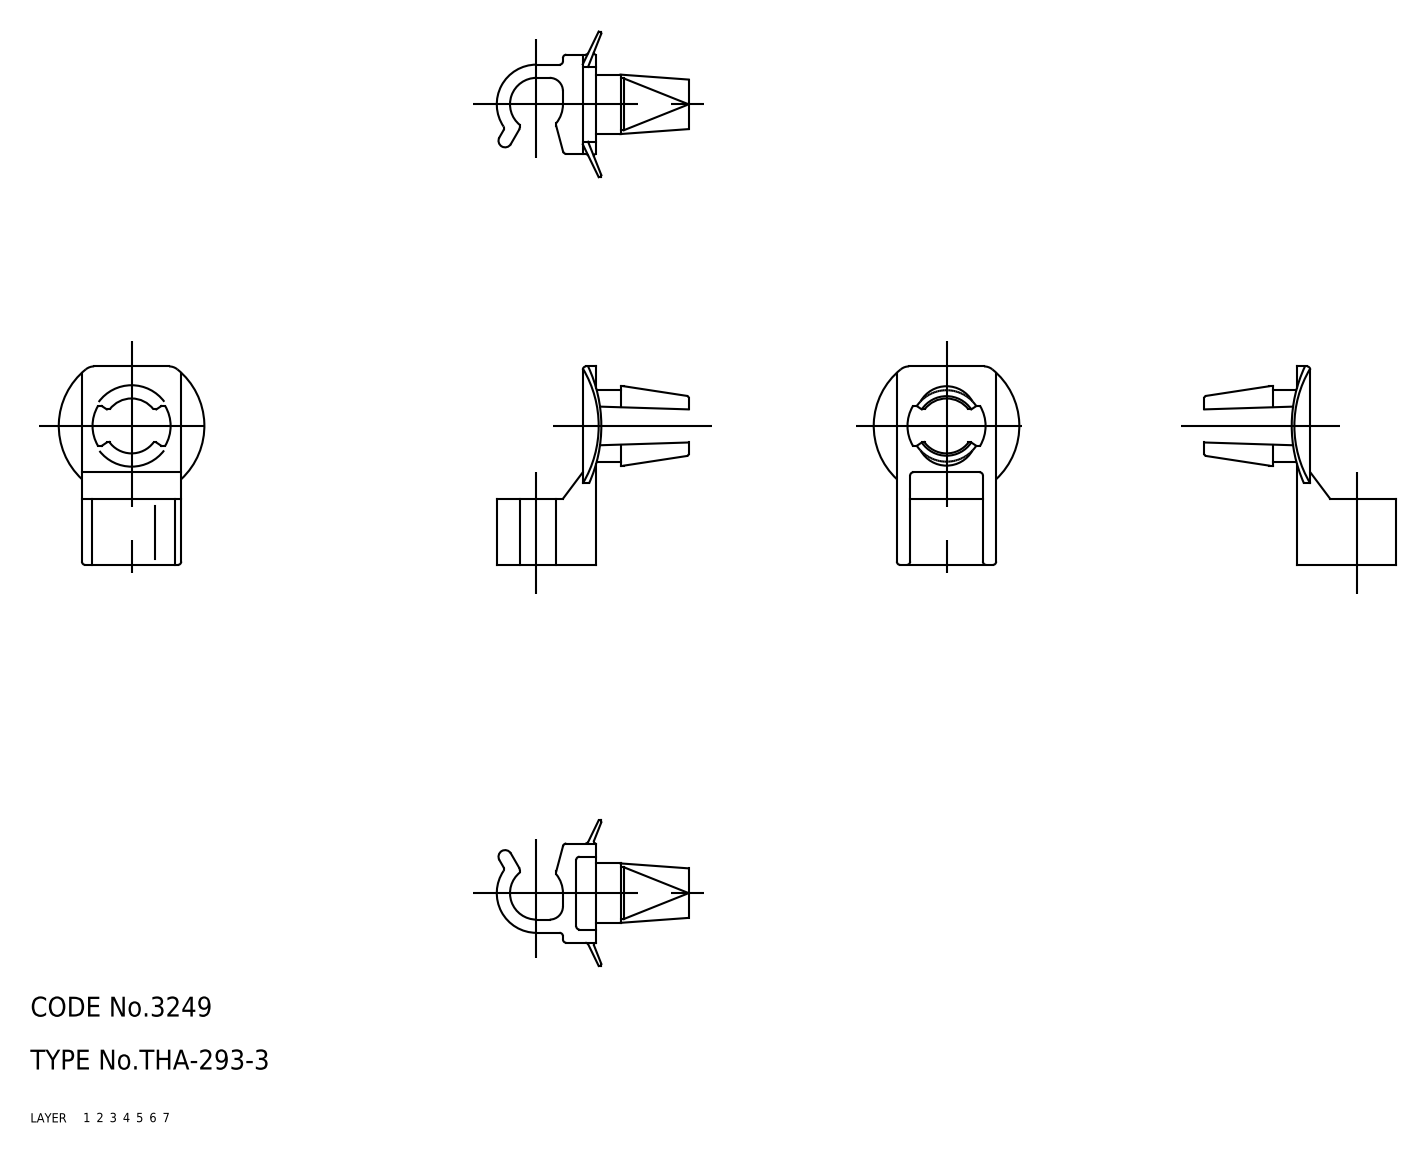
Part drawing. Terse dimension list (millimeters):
name: holder
written by: CADfix (AUTOMOTIVE_DESIGN)
unit: mm
bodies: 1 solid, 91 faces (0 planar, 0 cylindrical, 91 other)
size: 30 × 29 × 22
volume: 1 646 mm³; area: 2 293 mm²
